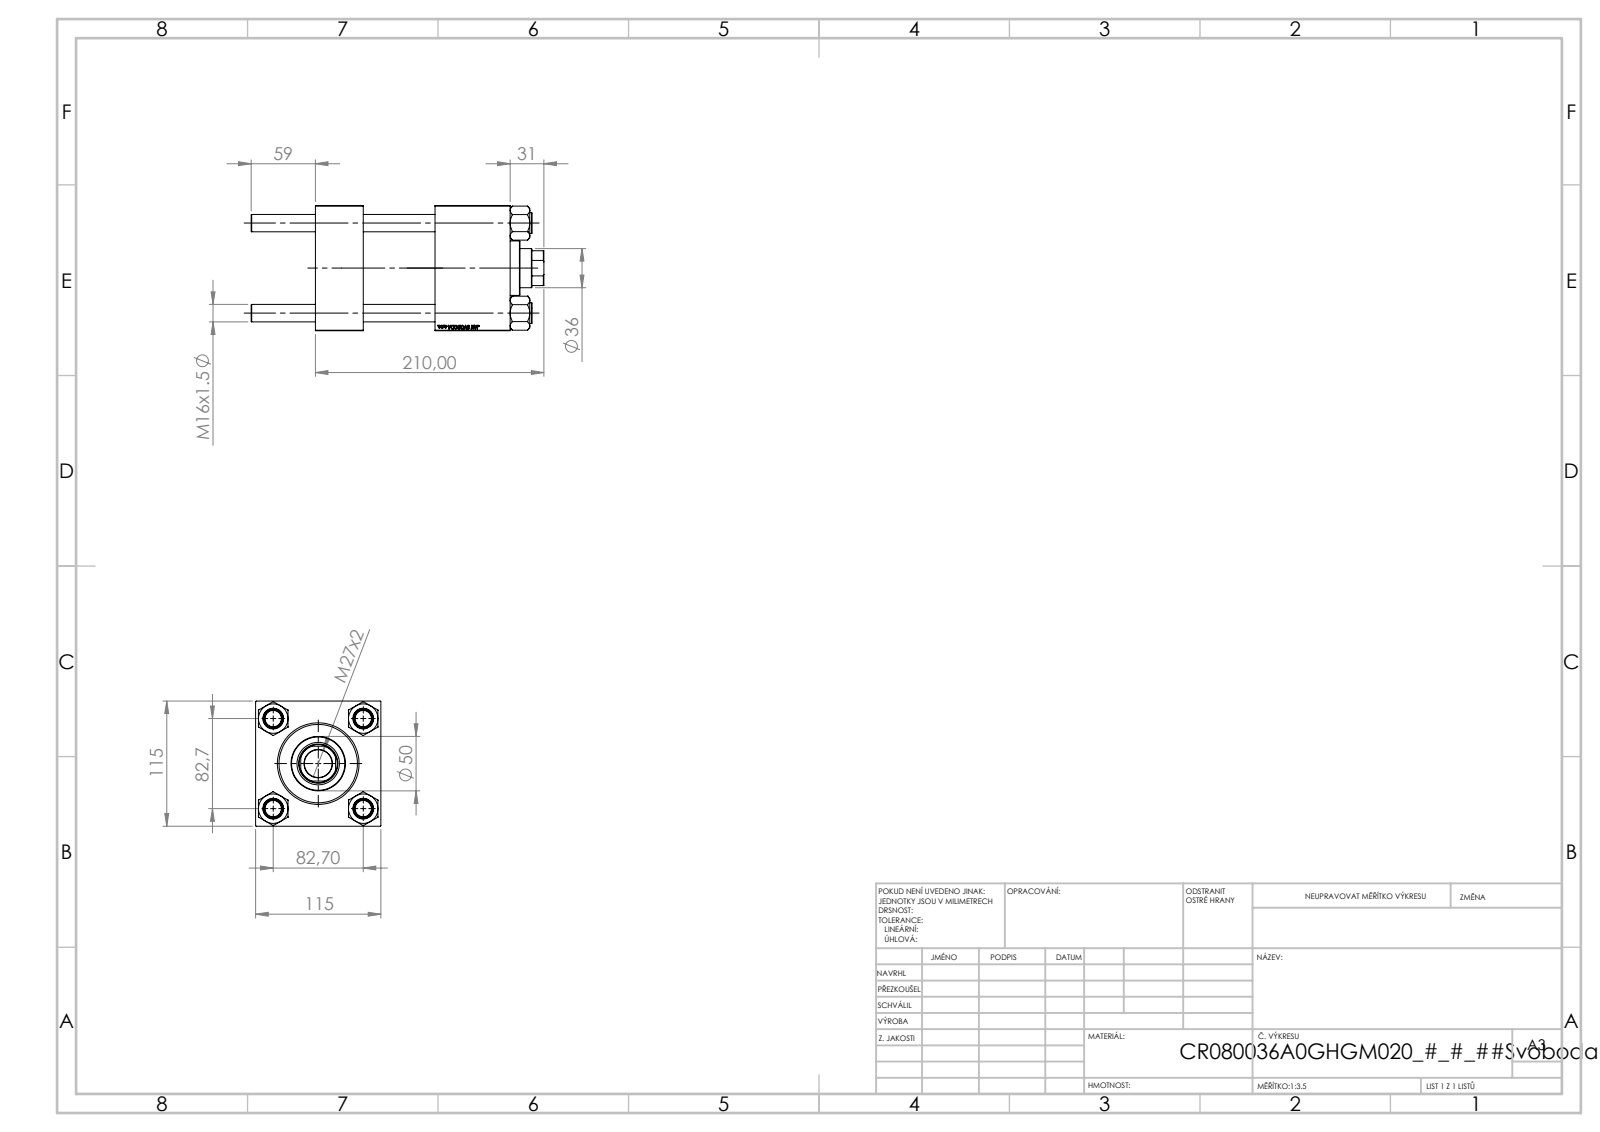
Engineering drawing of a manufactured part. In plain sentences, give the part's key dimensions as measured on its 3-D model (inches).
The part is named "V215CR_BODY_A; CR025_012_A_0_G_A_G_M_020_+#_##_TYCINKA; NUT_M5; V215CR_VCP (+1 more)". Its 3-D file was written by "SolidWorks 2019 (CONFIG_CONTROL_DESIGN)". It is 11 solids with 1182 faces: 568 planar, 78 cylindrical and 536 other. Overall it measures 10.591 by 4.528 by 4.528 inches. Its volume is 113.9 cubic inches and its surface area 456.6 square inches. Round holes: 4 of diameter 0.63, 2 of diameter 0.276, 2 of diameter 1.041, 2 of diameter 1.378, 1 of diameter 1.004, 1 of diameter 1.417, 1 of diameter 1.535, 1 of diameter 2.402, 1 of diameter 2.835, 1 of diameter 3.15. Round bosses or shafts: 4 of diameter 0.748, 1 of diameter 3.386, 1 of diameter 1.969. Partial cylindrical surfaces (rounded edges, fillets, slot ends): 1 of radius 0.689. The main face-to-face distances are 4.528, 1.732, 7.047, 5.315, 4.331, 2.598, 2.717, 0.787, 3.504, 5.917. The hole center spacings are 2.302, 3.256, 4.605, 4.37.
